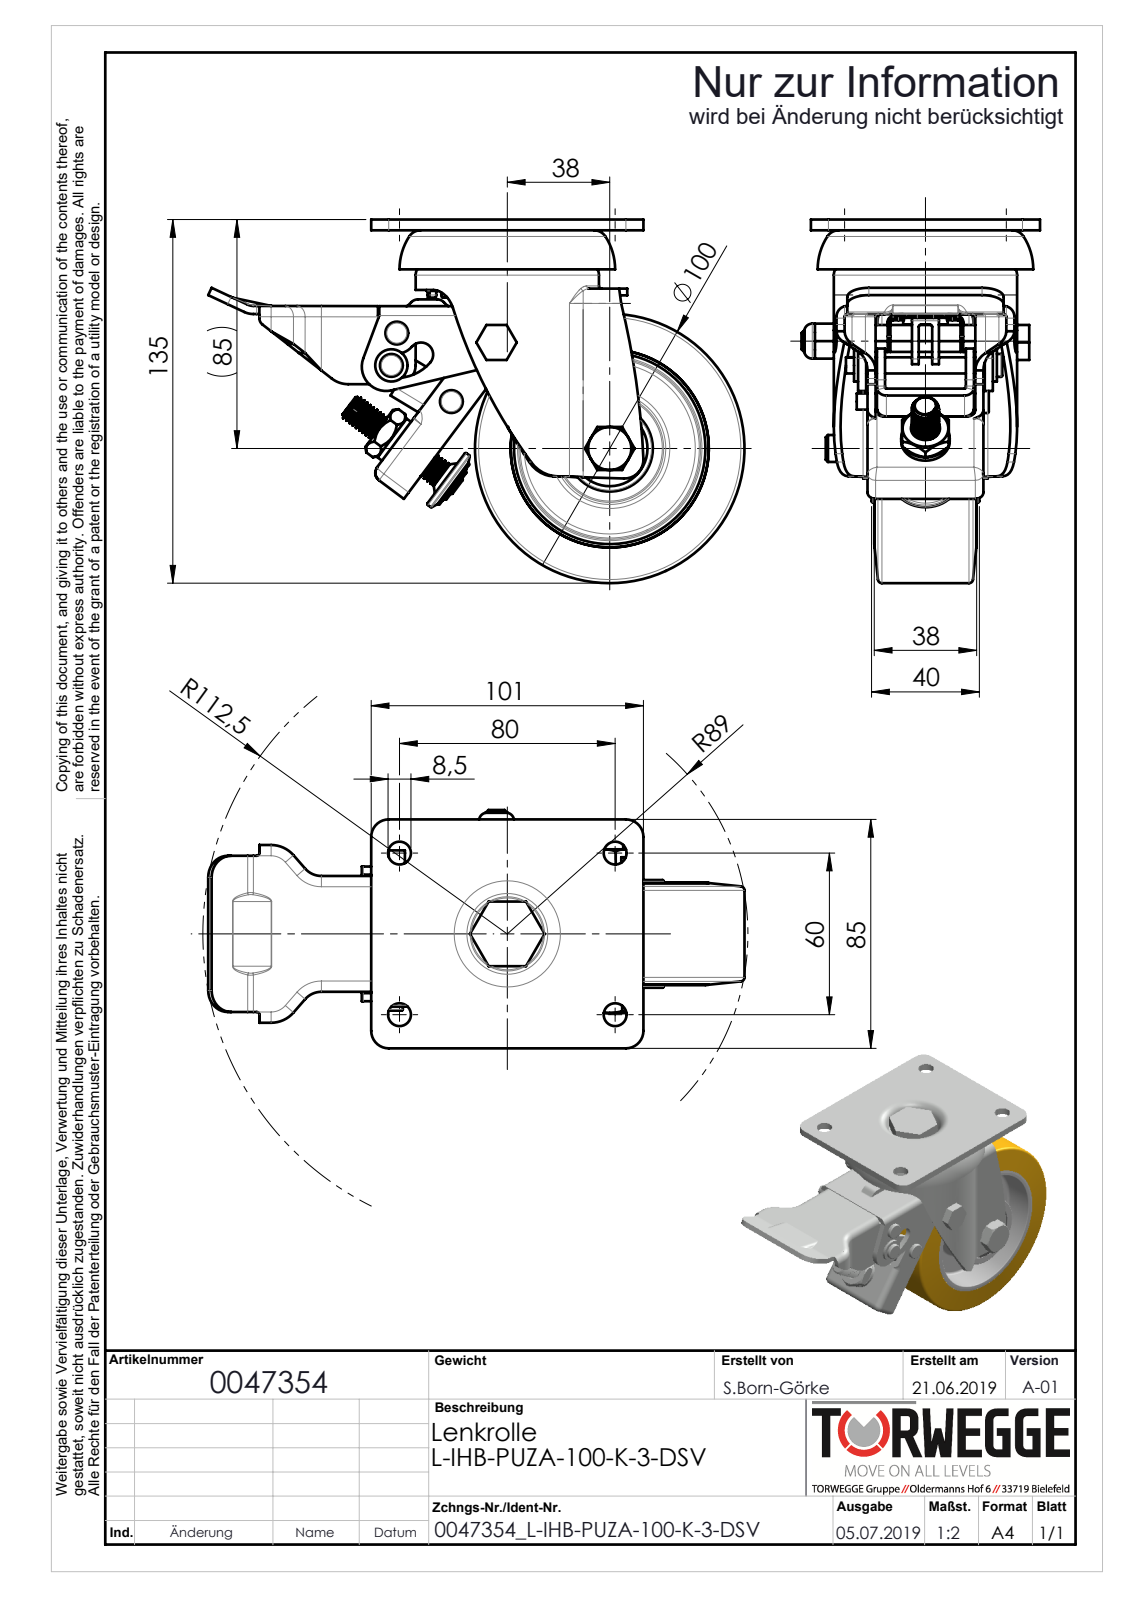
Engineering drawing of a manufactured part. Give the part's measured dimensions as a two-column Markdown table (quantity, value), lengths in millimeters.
| quantity | value |
| --- | --- |
| part name | 0047354_L-IHB-PUZA-100-K-3-DSV_(A-01) |
| STEP written by | SolidWorks 2018 (AUTOMOTIVE_DESIGN) |
| units | millimeters |
| bodies | 0 solids, 925 faces (306 planar, 381 cylindrical, 238 other) |
| overall size | 198.98 × 135 × 88.5 |
| round holes (diameter × count) | 8.5 × 6, 4 × 3, 6.5 × 3, 5 × 1, 10 × 1, 10.2 × 1, 10.5 × 1, 12 × 1, 28 × 1, 32 × 1 |
| round bosses / shafts (diameter × count) | 8.5 × 3, 6 × 3, 18 × 2, 12 × 2, 100 × 1, 68 × 1, 24 × 1, 20 × 1 |
| partial cylindrical surfaces (radius × count) | 1 × 42, 3.5 × 11, 4 × 9, 0.5 × 8, 8 × 7, 2 × 6, 3 × 6, 5 × 4 |
| main face-to-face distances | 3, 1.5, 2, 43.5, 3.5, 4, 40, 0.5, 1, 4.5 |
| hole center spacings | 60, 80, 100, 12.16, 26.01, 27.99, 32.5, 37.12 |
